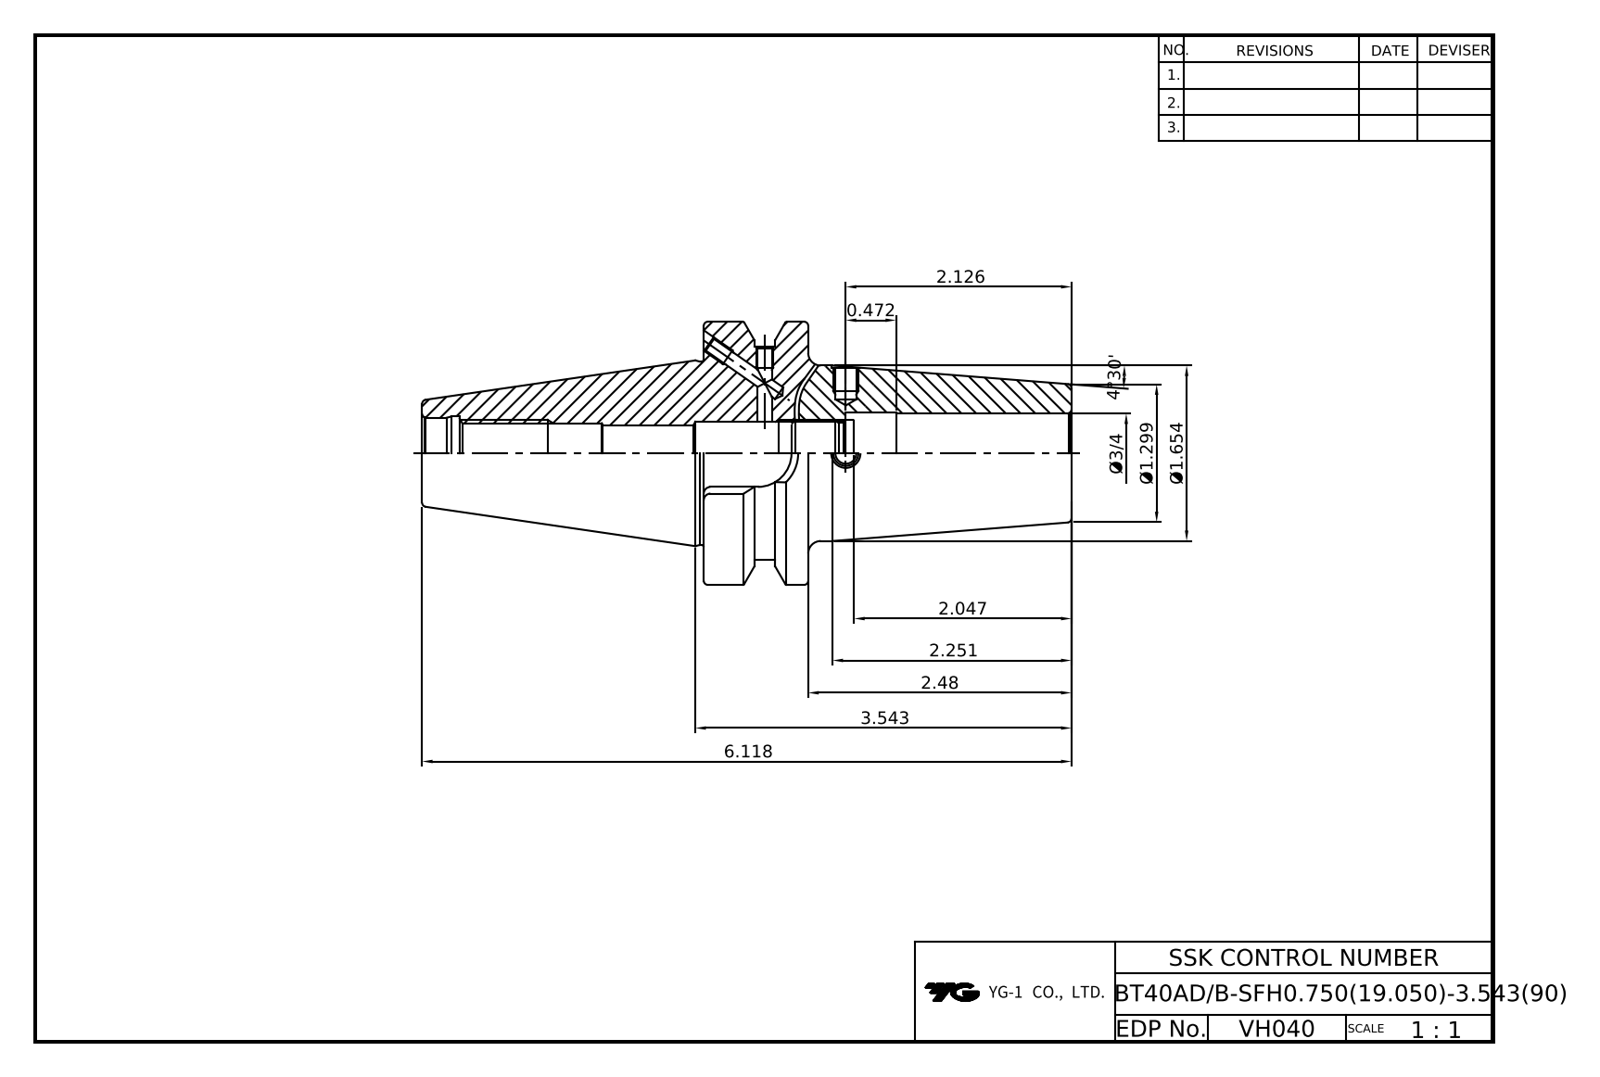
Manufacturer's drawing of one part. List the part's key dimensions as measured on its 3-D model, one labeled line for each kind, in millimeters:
Part name (STEP PRODUCT): LO-BT40ADB-SFH19.05-90
STEP written by: Autodesk Inventor 2020 (AUTOMOTIVE_DESIGN)
Units: millimetres
Bodies: 1 solid, 69 faces (21 planar, 28 cylindrical, 20 other)
Overall size (bounding box): 155.4 × 63 × 63
Volume: 172 347 mm³ · Surface area: 33 881 mm²
Round holes (diameter × count): ⌀3.24 ×4, ⌀4 ×4, ⌀13.5 ×1, ⌀13.84 ×1, ⌀14.92 ×1, ⌀17 ×1, ⌀17.6 ×1, ⌀19.05 ×1, ⌀19.65 ×1
Round bosses / shafts (diameter × count): ⌀63 ×1, ⌀51 ×1, ⌀44 ×1, ⌀42 ×1
Partial cylindrical surfaces — rounded edges, fillets, slot ends (radius × count): R8.05 ×1
Main face-to-face distances: 25, 88, 63, 45.2, 92.4, 9, 17.1, 7.9, 70.9, 12.1
